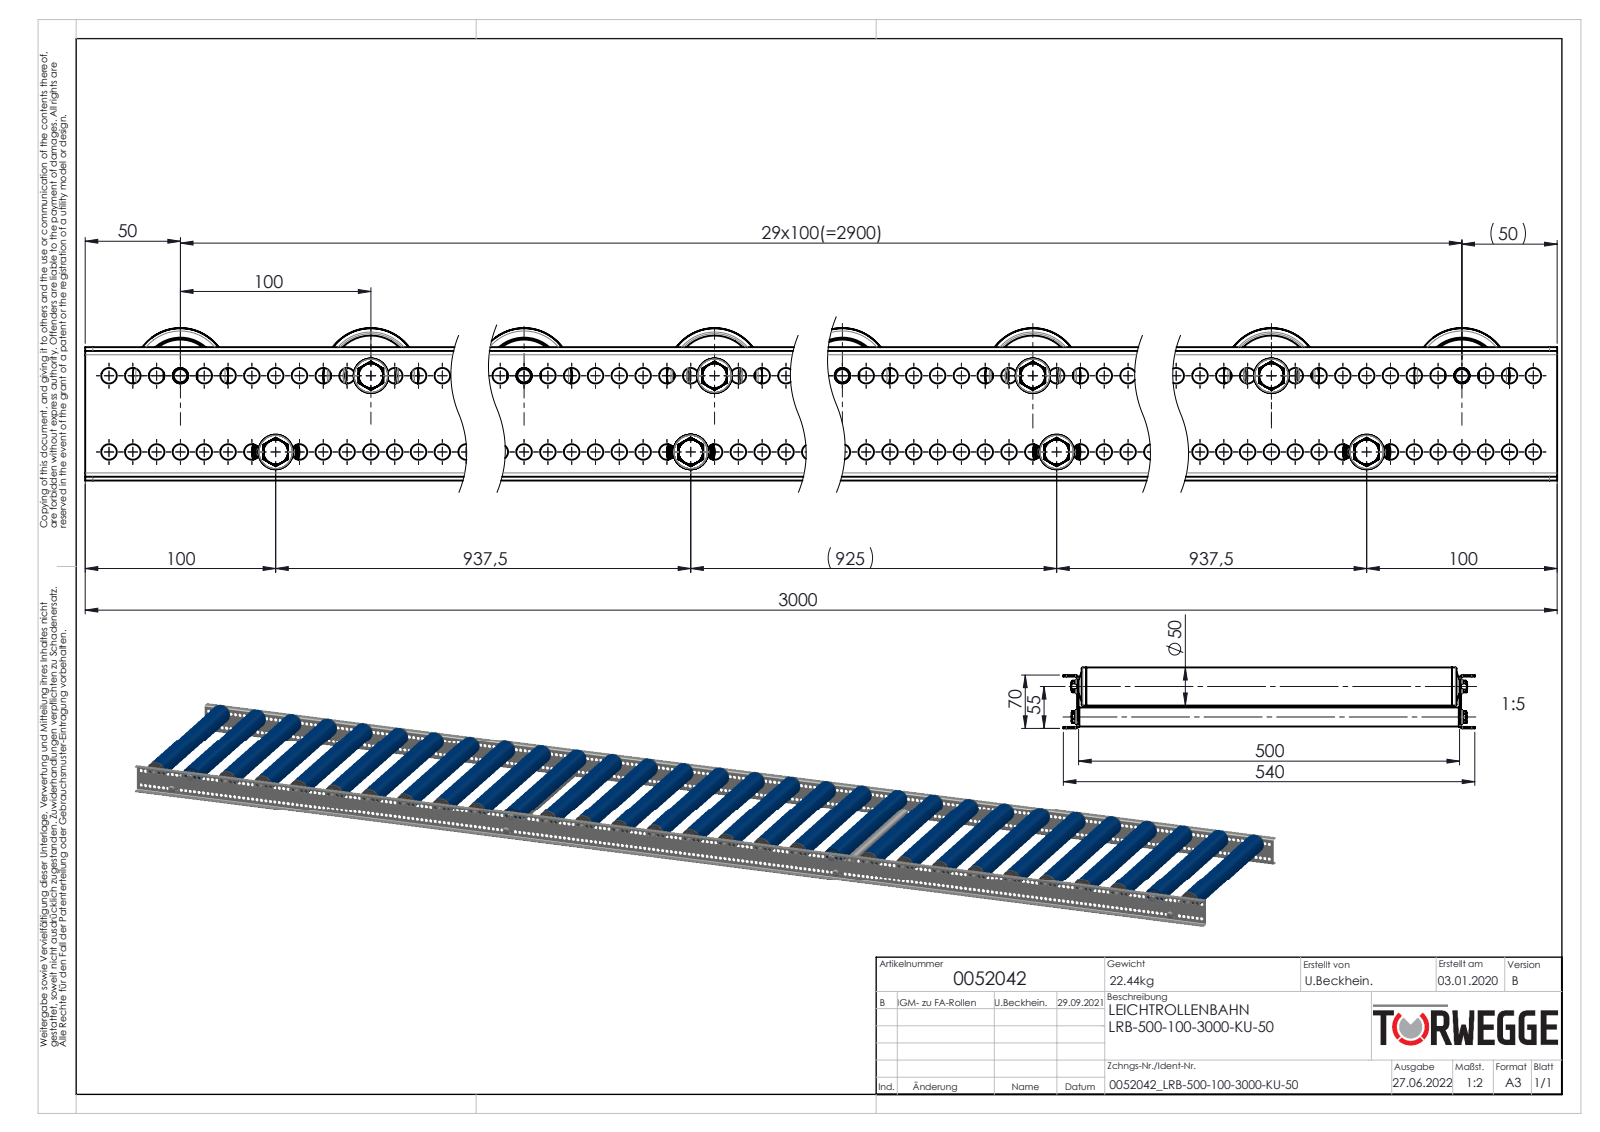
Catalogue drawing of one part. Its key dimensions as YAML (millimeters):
part_name: "0026266_Typ-KUT100-50x2,8-12; Sicherungsring_DIN471_8x0.8_Circlip DIN 471 - 8 x 0.8; 0052042; KUT100-50x2,8-KB-A8-FA_KFG_0034515_KUT100-50x2,8-KB-A8-FA-EL=500 (+8 more)"
step_written_by: "SolidWorks 2020 (AUTOMOTIVE_DESIGN)"
units: millimeters
bodies: {solids: 529, faces: 10474, planar: 2574, cylindrical: 4860, other: 3040}
overall_size: [3000, 540, 80]
volume: 10070000
surface_area: 7565000
round_holes:
  - {diameter: 8.2, count: 478}
  - {diameter: 7.6, count: 26}
  - {diameter: 8, count: 26}
  - {diameter: 25, count: 26}
  - {diameter: 30, count: 26}
  - {diameter: 35, count: 26}
  - {diameter: 39.4, count: 26}
  - {diameter: 40, count: 26}
  - {diameter: 6.8, count: 8}
  - {diameter: 12, count: 4}
  - {diameter: 12.1, count: 4}
  - {diameter: 16, count: 4}
round_bosses_or_shafts:
  - {diameter: 50, count: 30}
  - {diameter: 44.4, count: 26}
  - {diameter: 38, count: 26}
  - {diameter: 36, count: 26}
  - {diameter: 33, count: 26}
  - {diameter: 22, count: 26}
  - {diameter: 21, count: 26}
  - {diameter: 25, count: 8}
partial_cylinders:
  - {radius: 0.6, count: 52}
  - {radius: 0.75, count: 52}
  - {radius: 2.45, count: 52}
  - {radius: 4.87, count: 26}
  - {radius: 7, count: 26}
  - {radius: 2.5, count: 16}
  - {radius: 4, count: 8}
  - {radius: 2, count: 4}
face_to_face_distances: [2, 502, 68, 500, 504, 70, 66, 492, 6, 12]
hole_center_spacings: [12.5, 25, 37.5, 50, 62.5, 75, 87.5, 100]
